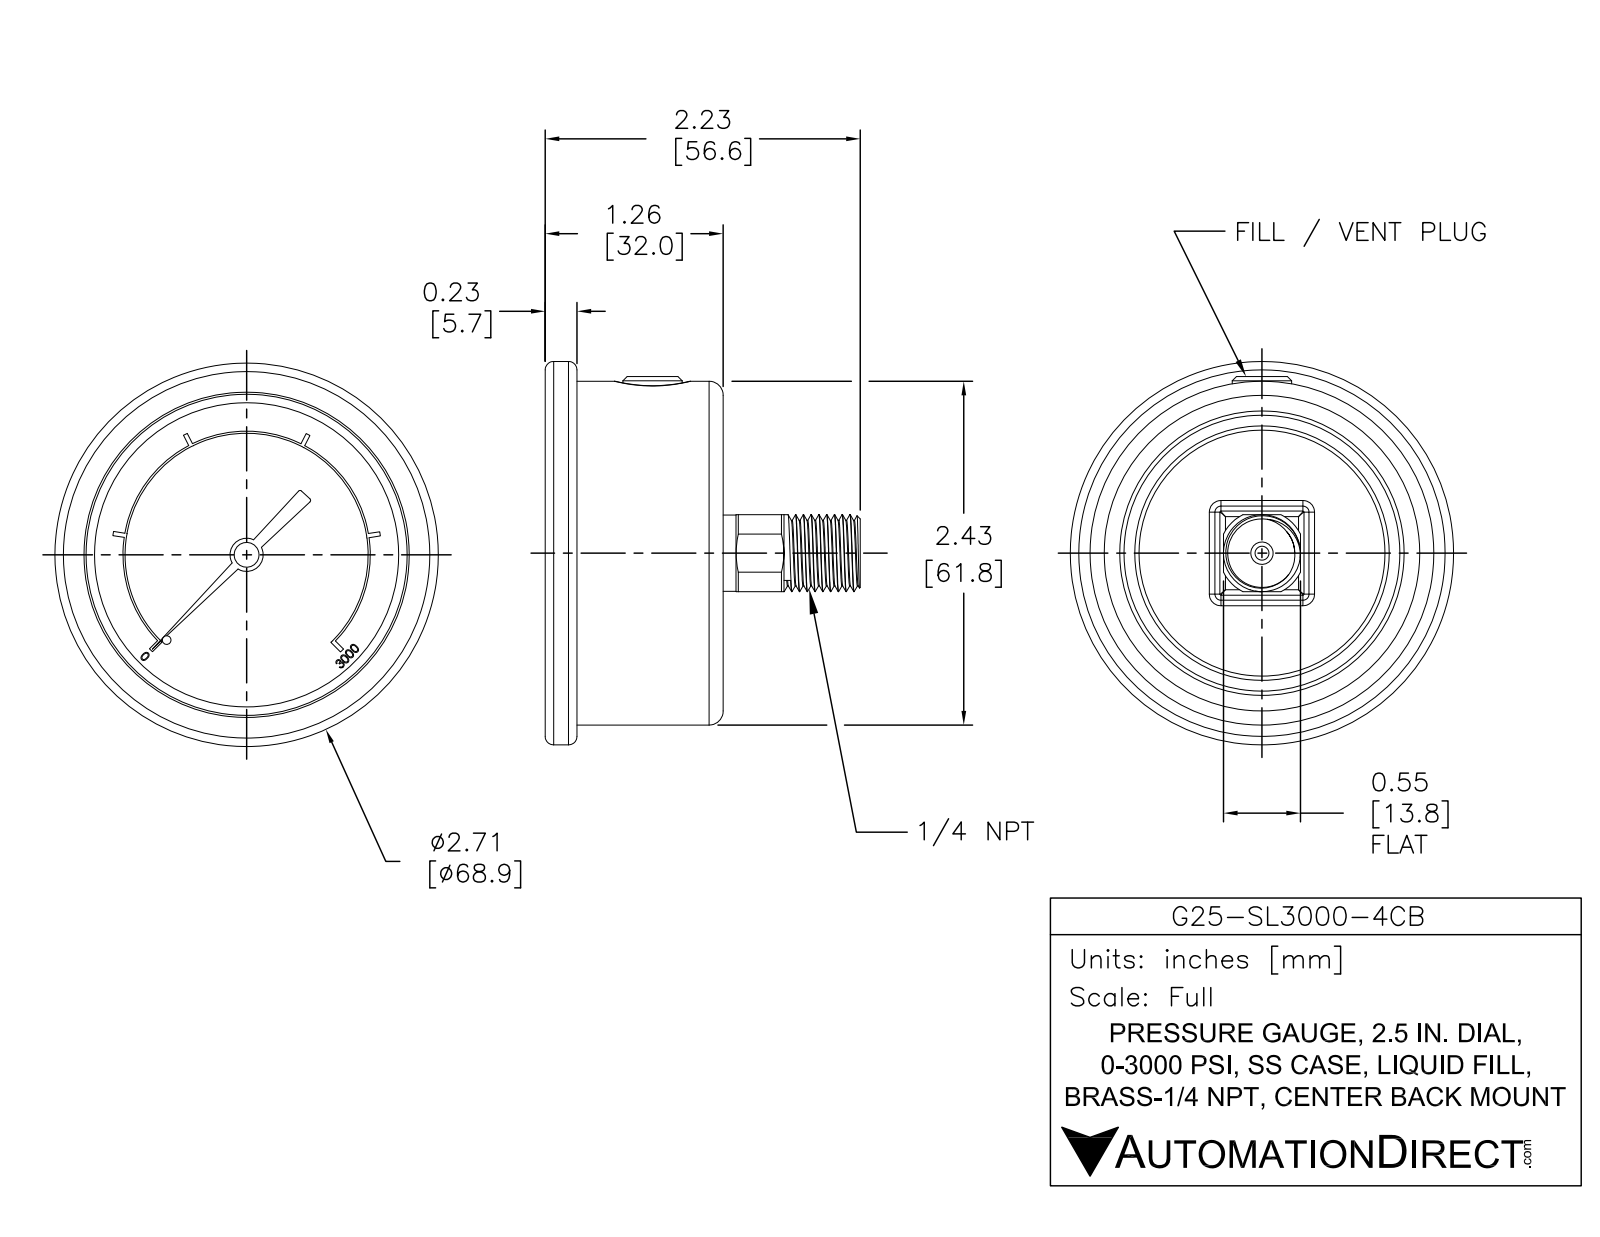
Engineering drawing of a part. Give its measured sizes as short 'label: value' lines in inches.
name: G25-SL3000-4CB
written by: SolidWorks 2021 (AUTOMOTIVE_DESIGN)
unit: in
bodies: 1 solid, 370 faces (207 planar, 83 cylindrical, 80 other)
size: 2.713 × 2.713 × 2.23
volume: 5.168 in³; area: 24.83 in²
holes: 1× ⌀0.071, 1× ⌀0.098, 1× ⌀2.272
bosses: 1× ⌀2.713, 1× ⌀2.433, 1× ⌀0.545, 1× ⌀0.54, 1× ⌀0.42, 1× ⌀0.235, 1× ⌀0.176, 1× ⌀0.14
rounds: 8× R0.06, 2× R0.015, 1× R0.304, 1× R0.86, 1× R0.875
face distances: 0.95, 1.2, 0.25, 0.06, 1.01, 1.26, 1.035, 0.975, 0.025, 0.225
